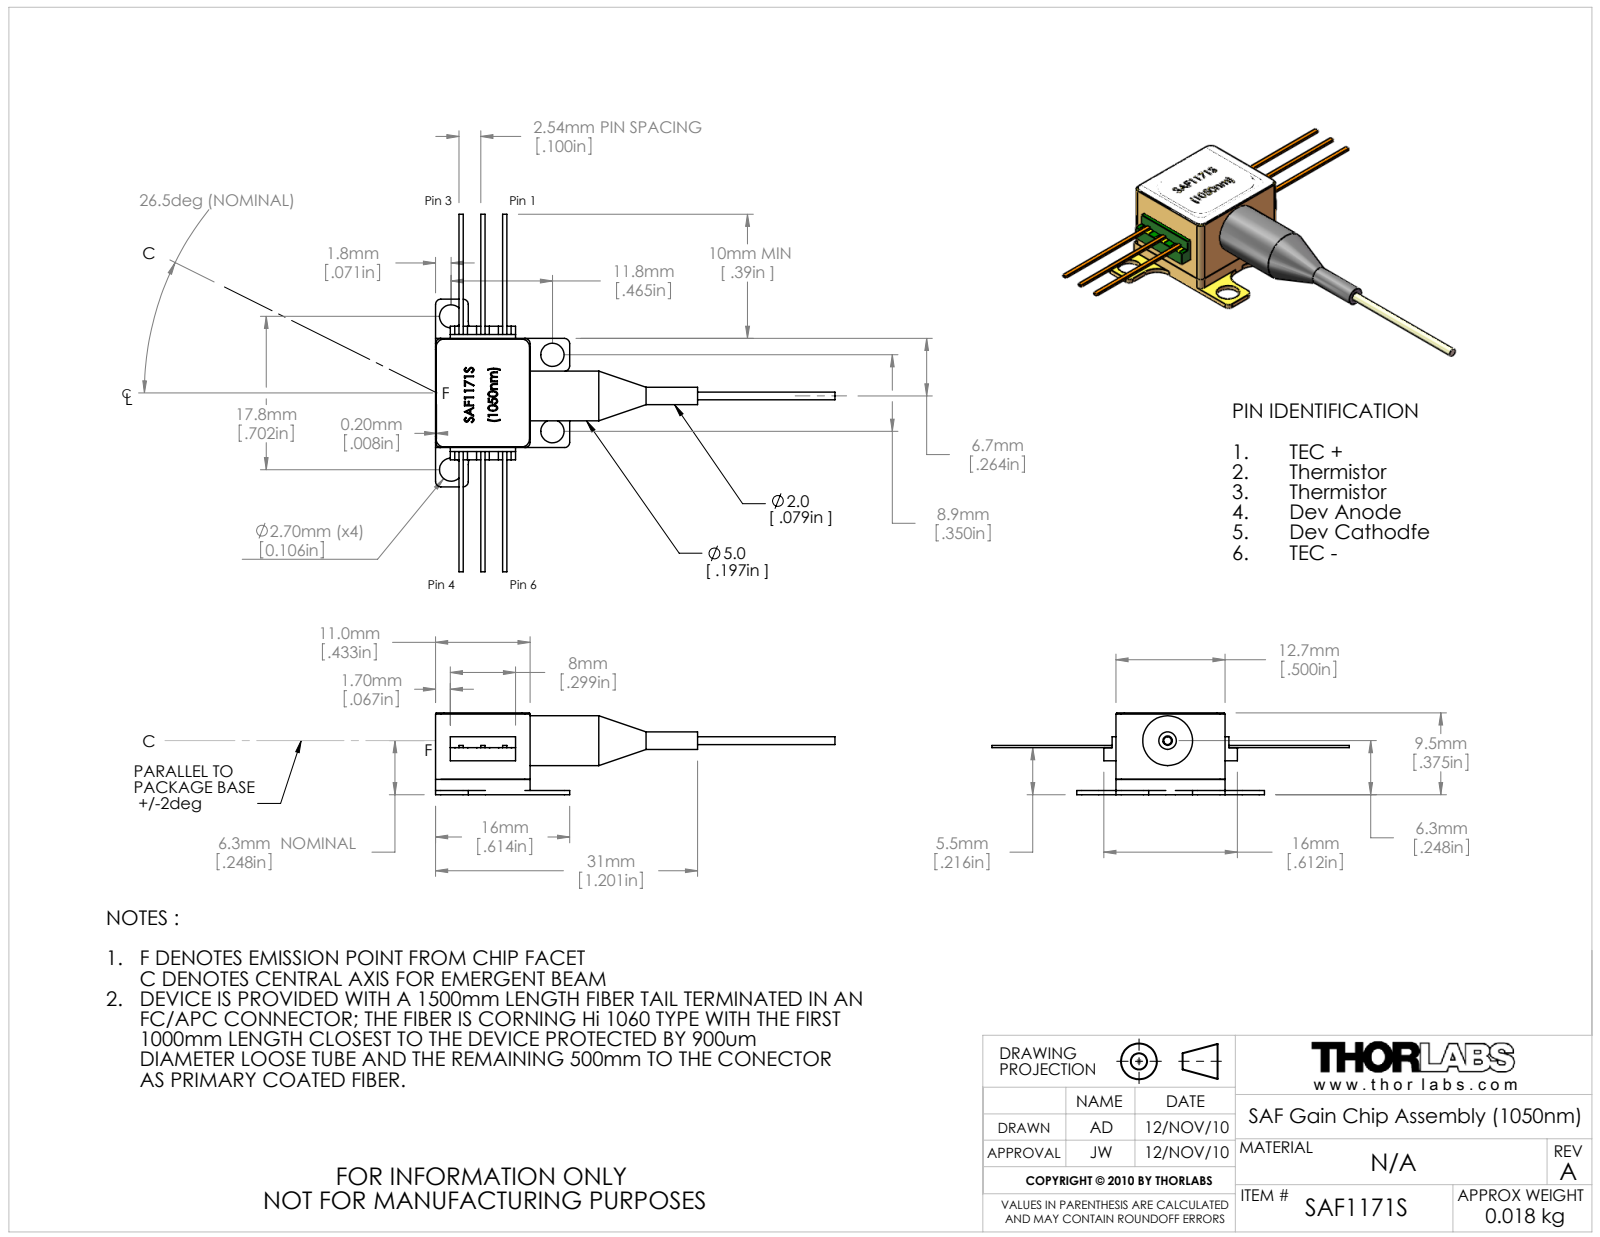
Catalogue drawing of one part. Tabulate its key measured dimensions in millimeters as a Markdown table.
| quantity | value |
| --- | --- |
| part name | 1171S OSA; SAF1171S 1050nm Lid_REV 2 - Mit Text; Short tail section; 21470-E0W (+7 more) |
| STEP written by | SolidWorks 2009 (AUTOMOTIVE_DESIGN) |
| units | millimeters |
| bodies | 15 solids, 454 faces (299 planar, 70 cylindrical, 85 other) |
| overall size | 46.5 × 41.6 × 9.53 |
| volume | 931 mm³ |
| surface area | 2 424 mm² |
| round holes (diameter × count) | 2.7 × 4, 1.1 × 1, 2.08 × 1, 3.18 × 1, 4.1 × 1 |
| round bosses / shafts (diameter × count) | 5.8 × 1, 3.45 × 1, 2.04 × 1, 0.9 × 1 |
| partial cylindrical surfaces (radius × count) | 0.6 × 12, 1 × 10, 0.13 × 4, 0.3 × 4, 0.9 × 4, 1.85 × 4, 2 × 4 |
| main face-to-face distances | 1, 1.6, 9.52, 7.92, 9.4, 7.6, 7.8, 1.45, 11.7, 1.8 |
| hole center spacings | 12.62, 17.83, 8.9, 17.84 |
